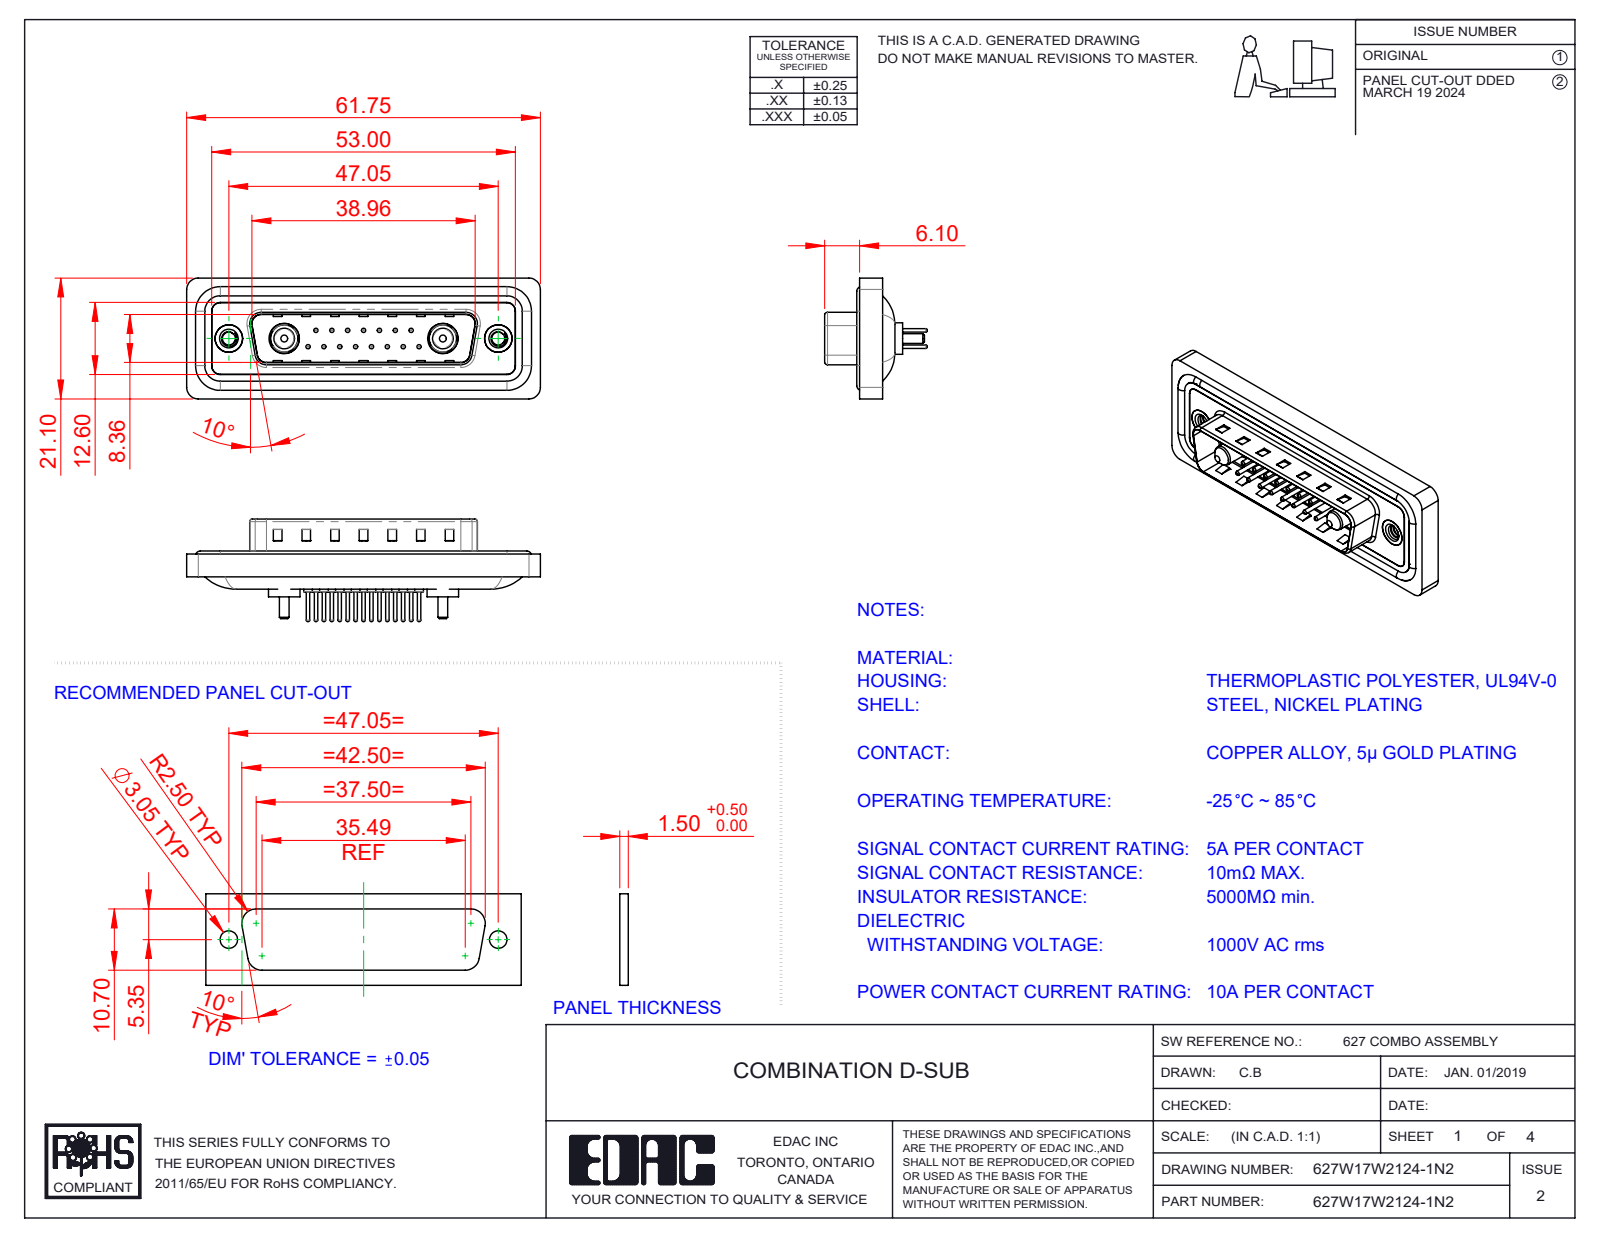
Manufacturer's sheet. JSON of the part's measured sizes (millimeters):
{"part_name": "627Combo Threaded Rivet_2; Power Pin_10A S; 627Combo Shell Front_25 Contacts; 627Combo Shell Rear_25 Contacts (+5 more)", "step_written_by": "SolidWorks 2023 (CONFIG_CONTROL_DESIGN)", "units": "millimeters", "bodies": {"solids": 26, "faces": 1116, "planar": 334, "cylindrical": 436, "other": 346}, "overall_size": [61.75, 21.1, 17.9], "volume_mm3": 7237, "surface_area_mm2": 11889, "round_holes": [[0.75, 15], [1.6, 15], [2, 15], [2.26, 2], [4, 2], [4.8, 2], [4.85, 2], [5, 2], [5.3, 2]], "round_bosses_or_shafts": [[1.5, 15], [0.6, 15], [1.6, 4], [5.5, 2], [5.2, 2], [4.9, 2], [4.75, 2], [3.75, 2]], "partial_cylinders_radius": [[1.5, 22], [2, 18], [0.5, 8], [1.6, 8], [0.25, 4], [0.6, 4], [0.65, 4], [0.9, 4]], "face_to_face_distances": [0.4, 1.5, 1.1, 1.6, 0.5, 3.1, 2.9, 0.82, 9.58, 4.1], "hole_center_spacings": [3.16, 2.77, 5.54, 8.31, 5.04, 7.49, 11.08, 5.03]}
